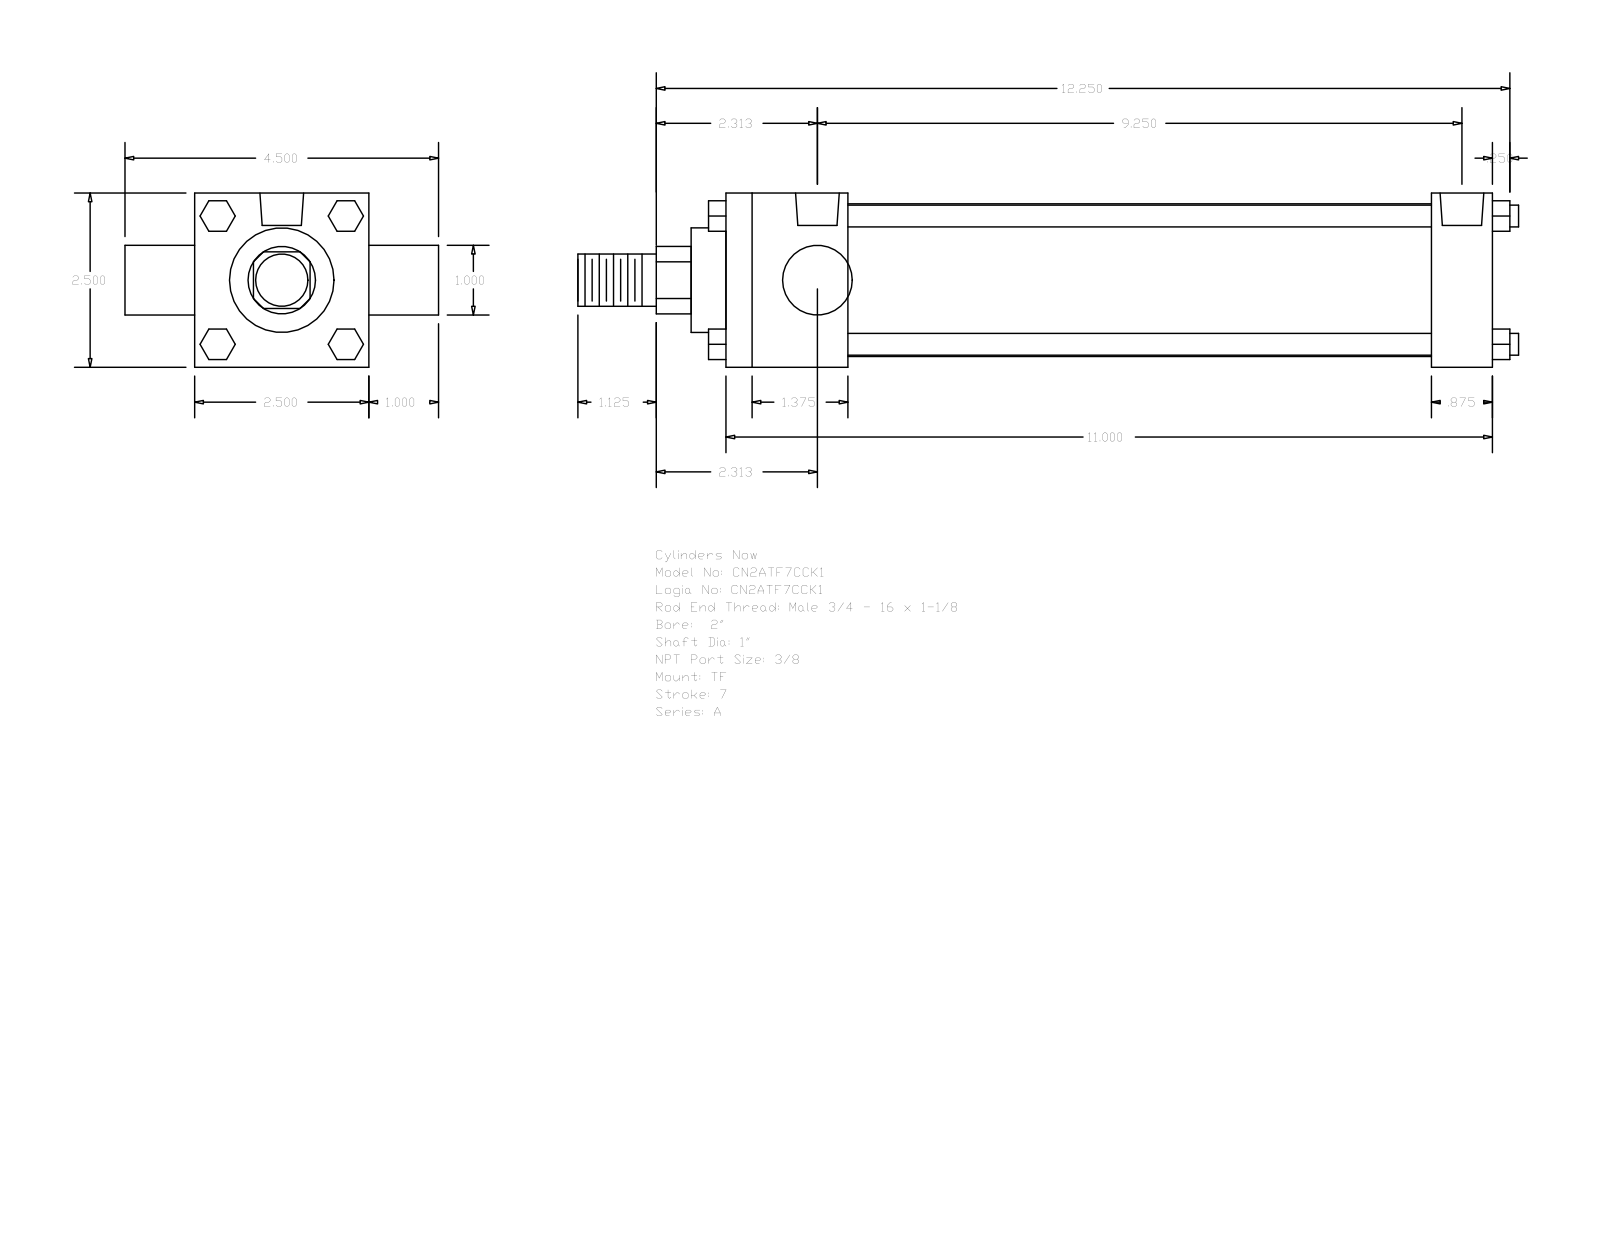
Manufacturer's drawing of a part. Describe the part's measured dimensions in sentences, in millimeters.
The part is named "A_TF__0200_1". Its 3-D file was written by "GSSL Pune (CONFIG_CONTROL_DESIGN)". It is 0 solids with 120 faces: 92 planar, 28 cylindrical and 0 other. Overall it measures 342.9 by 114.3 by 63.5 millimeters. Round holes: 3 of diameter 5.56, 2 of diameter 15.93. Round bosses or shafts: 4 of diameter 7.94, 2 of diameter 25.4, 1 of diameter 55.63, 1 of diameter 38.1, 1 of diameter 19.05. Partial cylindrical surfaces (rounded edges, fillets, slot ends): 1 of radius 12.29. The main face-to-face distances are 63.5, 279.4, 44.45, 257.17, 212.72, 234.95, 22.23, 25.4, 88.9, 292.1. The hole center spacings are 1.59, 3.98, 229.38, 230.97, 233.36, 234.95.
